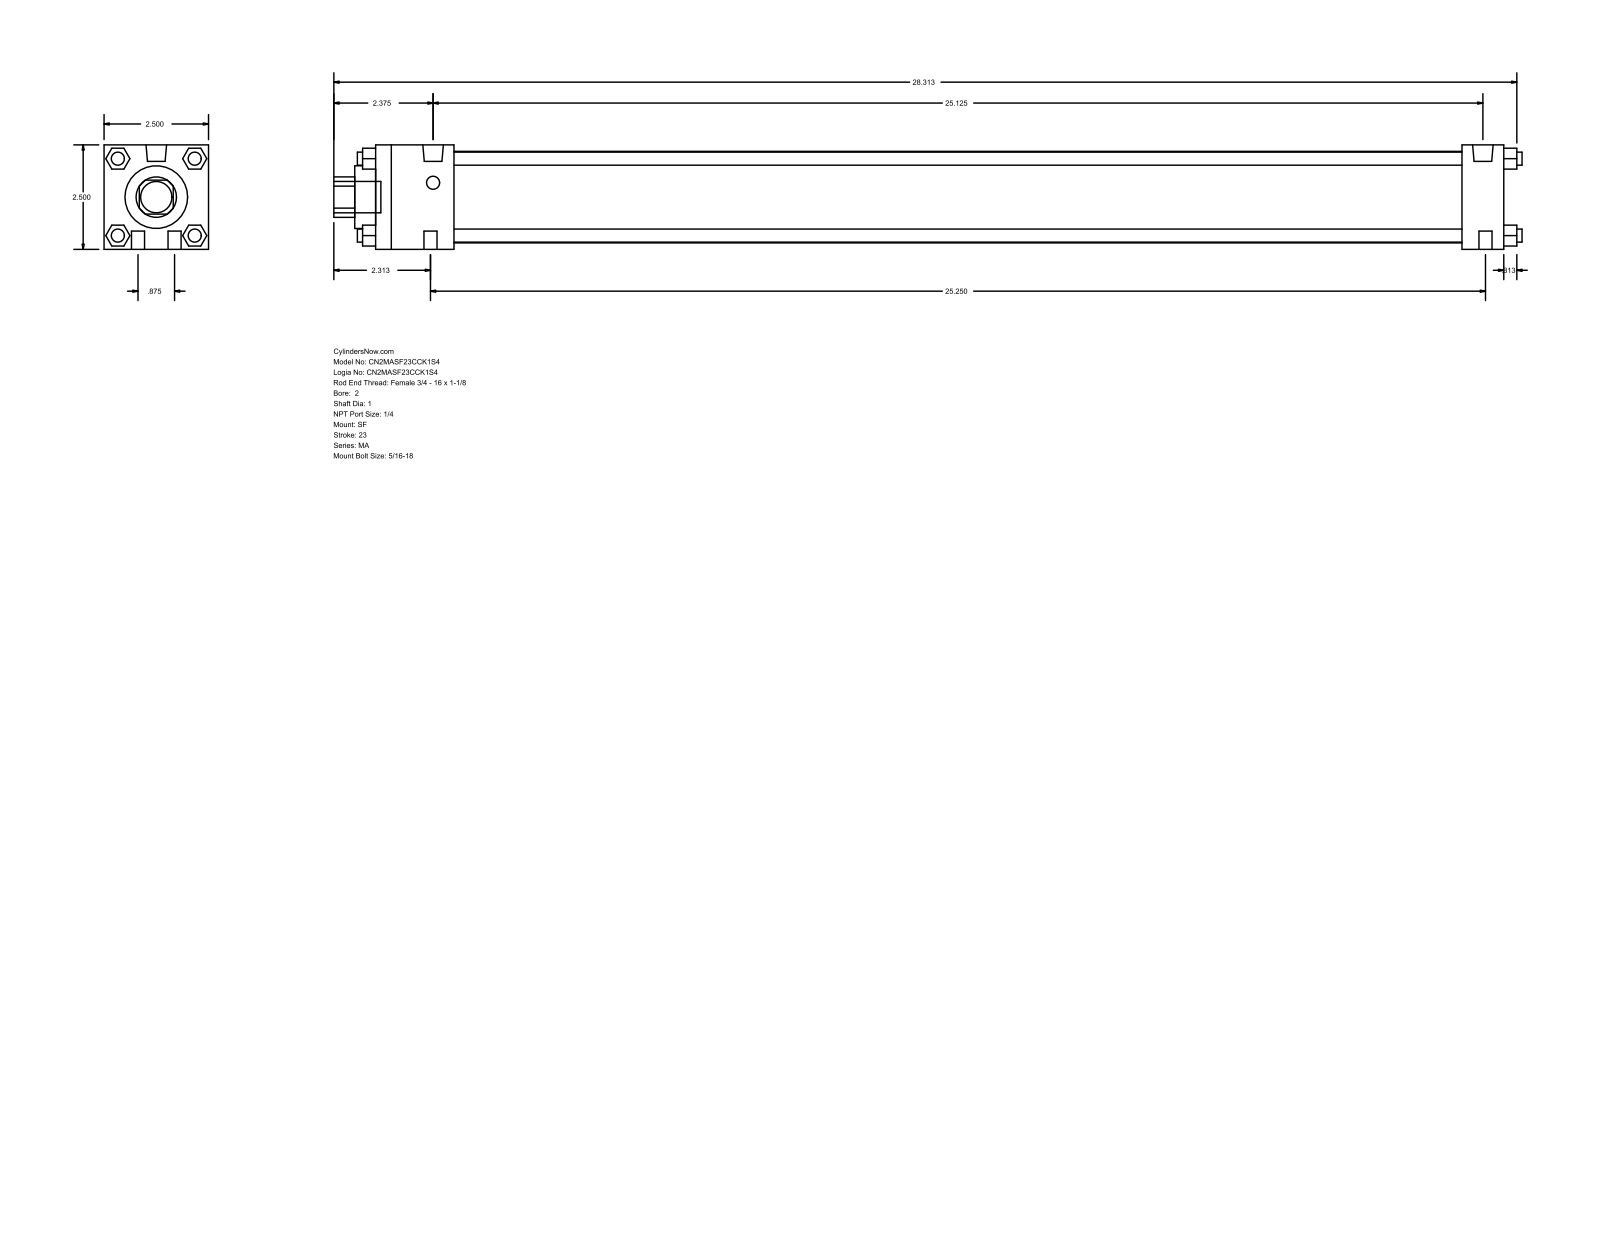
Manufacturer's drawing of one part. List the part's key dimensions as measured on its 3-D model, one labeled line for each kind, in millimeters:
Part name (STEP PRODUCT): MA_SF__0200_1
STEP written by: GSSL Pune (CONFIG_CONTROL_DESIGN)
Units: millimetres
Bodies: 0 solids, 124 faces (94 planar, 30 cylindrical, 0 other)
Overall size (bounding box): 722.31 × 63.5 × 63.5
Round holes (diameter × count): ⌀25.4 ×1, ⌀38.1 ×1, ⌀55.63 ×1
Round bosses / shafts (diameter × count): ⌀7.94 ×10, ⌀12.49 ×2, ⌀19.05 ×1
Partial cylindrical surfaces — rounded edges, fillets, slot ends (radius × count): R12.29 ×1
Main face-to-face distances: 63.5, 685.8, 12.7, 25.4, 660.4, 47.63, 612.77, 638.17, 40.47, 23.37
